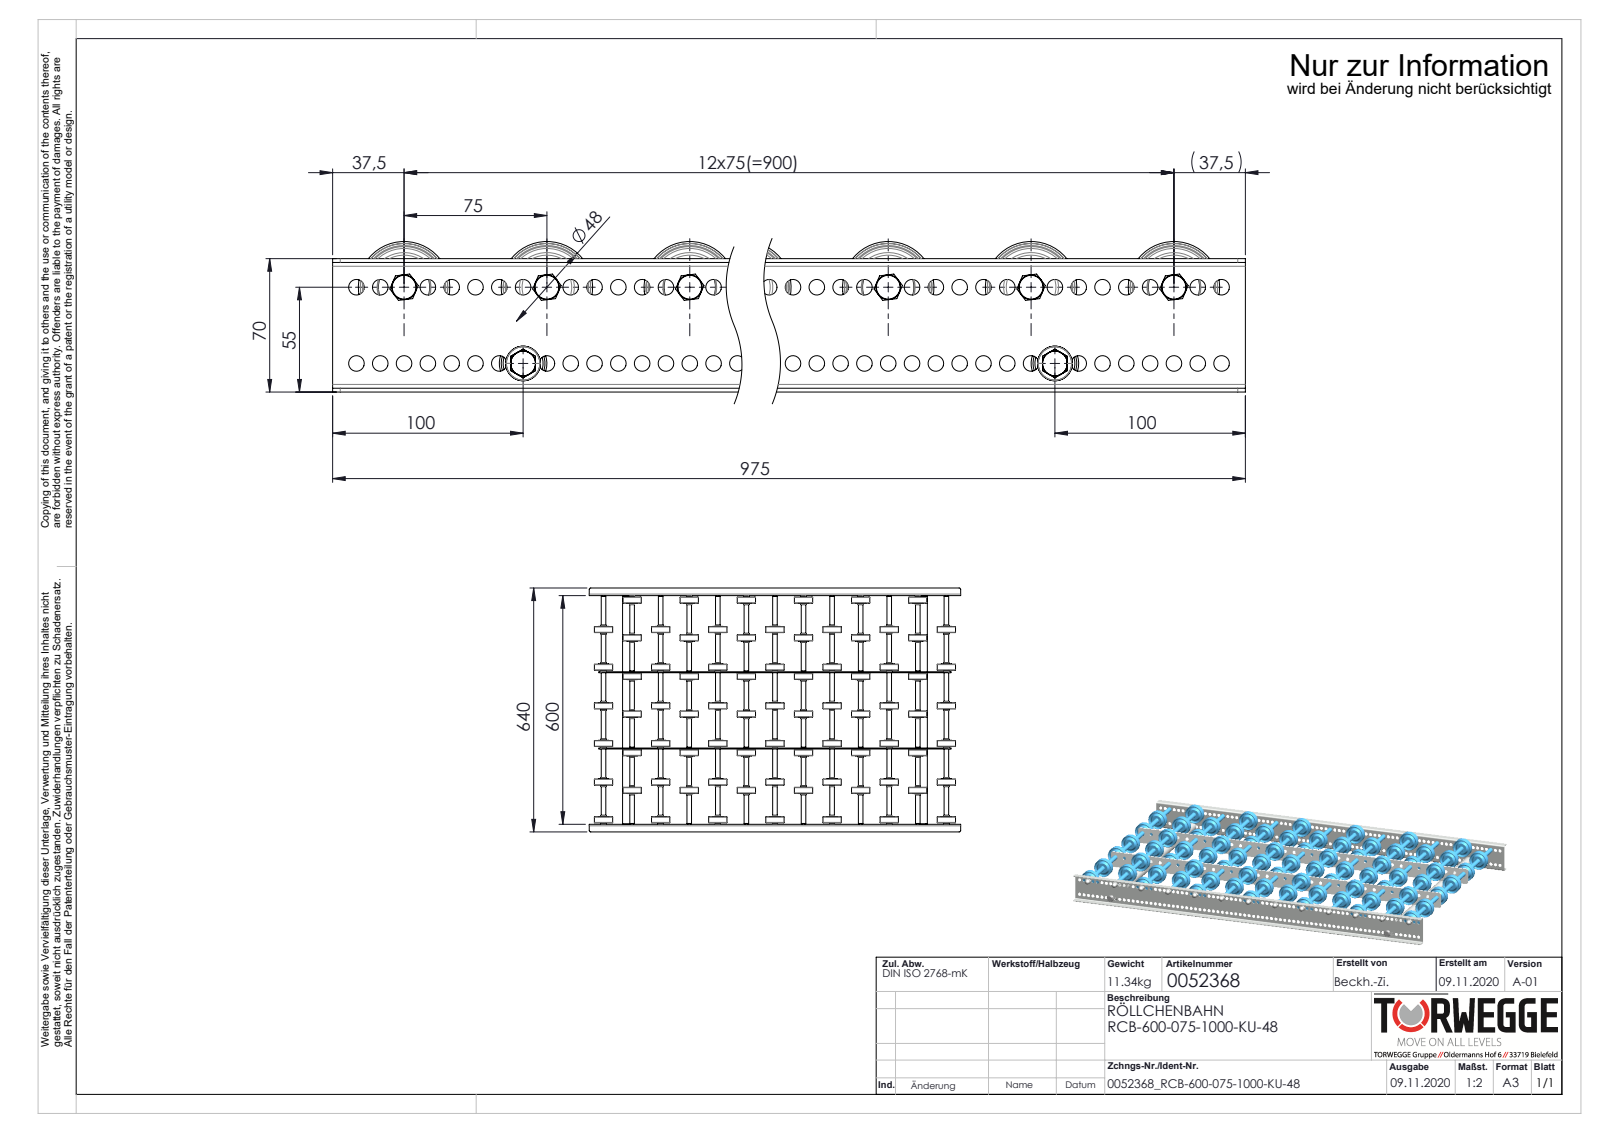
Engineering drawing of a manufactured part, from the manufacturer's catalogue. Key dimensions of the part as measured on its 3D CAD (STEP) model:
Part name (STEP PRODUCT): 0046278_KB-ROHR-12X1,75mm_KFG_L75; S100100_Längstraverse-42x2,5_S100101_Lngstraverse-RB-L975; Profil_LRB-20x70x20x2_KFG_S100213_U-PROFIL-20-70-20-2-LRB-L=975; Hutmutter_DIN_1587_M8 (+6 more)
STEP written by: SolidWorks 2020 (AUTOMOTIVE_DESIGN)
Units: millimetres
Bodies: 209 solids, 7746 faces (1380 planar, 2674 cylindrical, 3692 other)
Overall size (bounding box): 975 × 640 × 79
Volume: 2 902 000 mm³ · Surface area: 2 121 000 mm²
Round holes (diameter × count): ⌀8.2 ×154, ⌀8.5 ×37, ⌀6.65 ×13, ⌀9.65 ×13, ⌀13.7 ×13, ⌀6.8 ×2, ⌀21 ×2
Round bosses / shafts (diameter × count): ⌀8 ×15, ⌀48 ×13, ⌀27 ×13, ⌀12.7 ×13, ⌀12.5 ×13, ⌀12 ×13, ⌀25 ×2
Partial cylindrical surfaces — rounded edges, fillets, slot ends (radius × count): R4 ×8, R2 ×4, R5 ×4
Main face-to-face distances: 2, 200.1, 602, 2.5, 197.6, 68, 604, 600, 400.2, 201.8
Hole centre spacings: 12.5, 25, 37.5, 50, 62.5, 75, 87.5, 100
